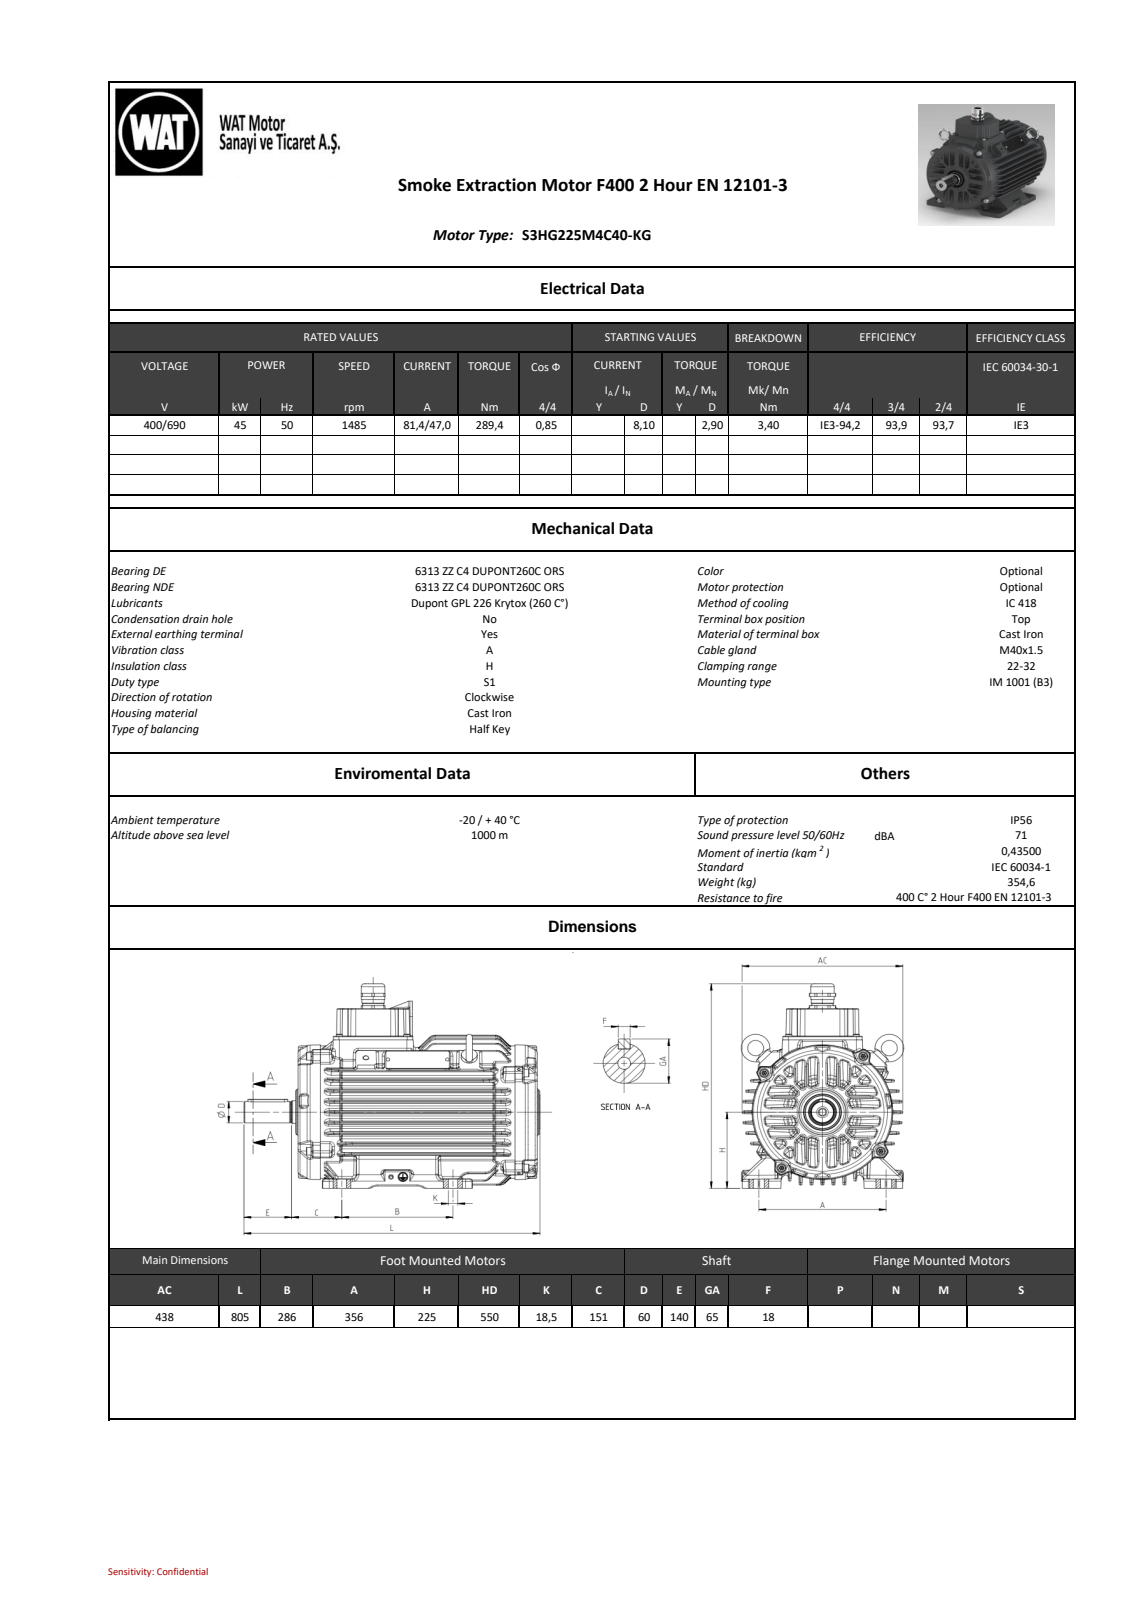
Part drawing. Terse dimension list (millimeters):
name: 260381480CFDz4kp
written by: SIEMENS PLM Software NX 11.0 (AUTOMOTIVE_DESIGN)
unit: mm
bodies: 0 solids, 7184 faces (934 planar, 1625 cylindrical, 4625 other)
size: 805 × 550 × 443
holes: 10× ⌀14, 5× ⌀6.8, 1× ⌀21, 1× ⌀32, 1× ⌀82, 1× ⌀88.33, 1× ⌀100
bosses: 8× ⌀30, 4× ⌀24, 4× ⌀23.67, 4× ⌀12, 2× ⌀35, 1× ⌀372, 1× ⌀76.67, 1× ⌀65
rounds: 328× R4, 234× R2, 147× R5, 136× R3, 82× R6, 44× R0.6, 18× R10, 16× R0.5
face distances: 17.32, 194.42, 159.69, 17.41, 34.89, 142.21, 17.48, 52.44, 124.66, 35.03
hole spacings: 198, 280.01, 68.76, 227.14, 324.38, 389.98, 396
